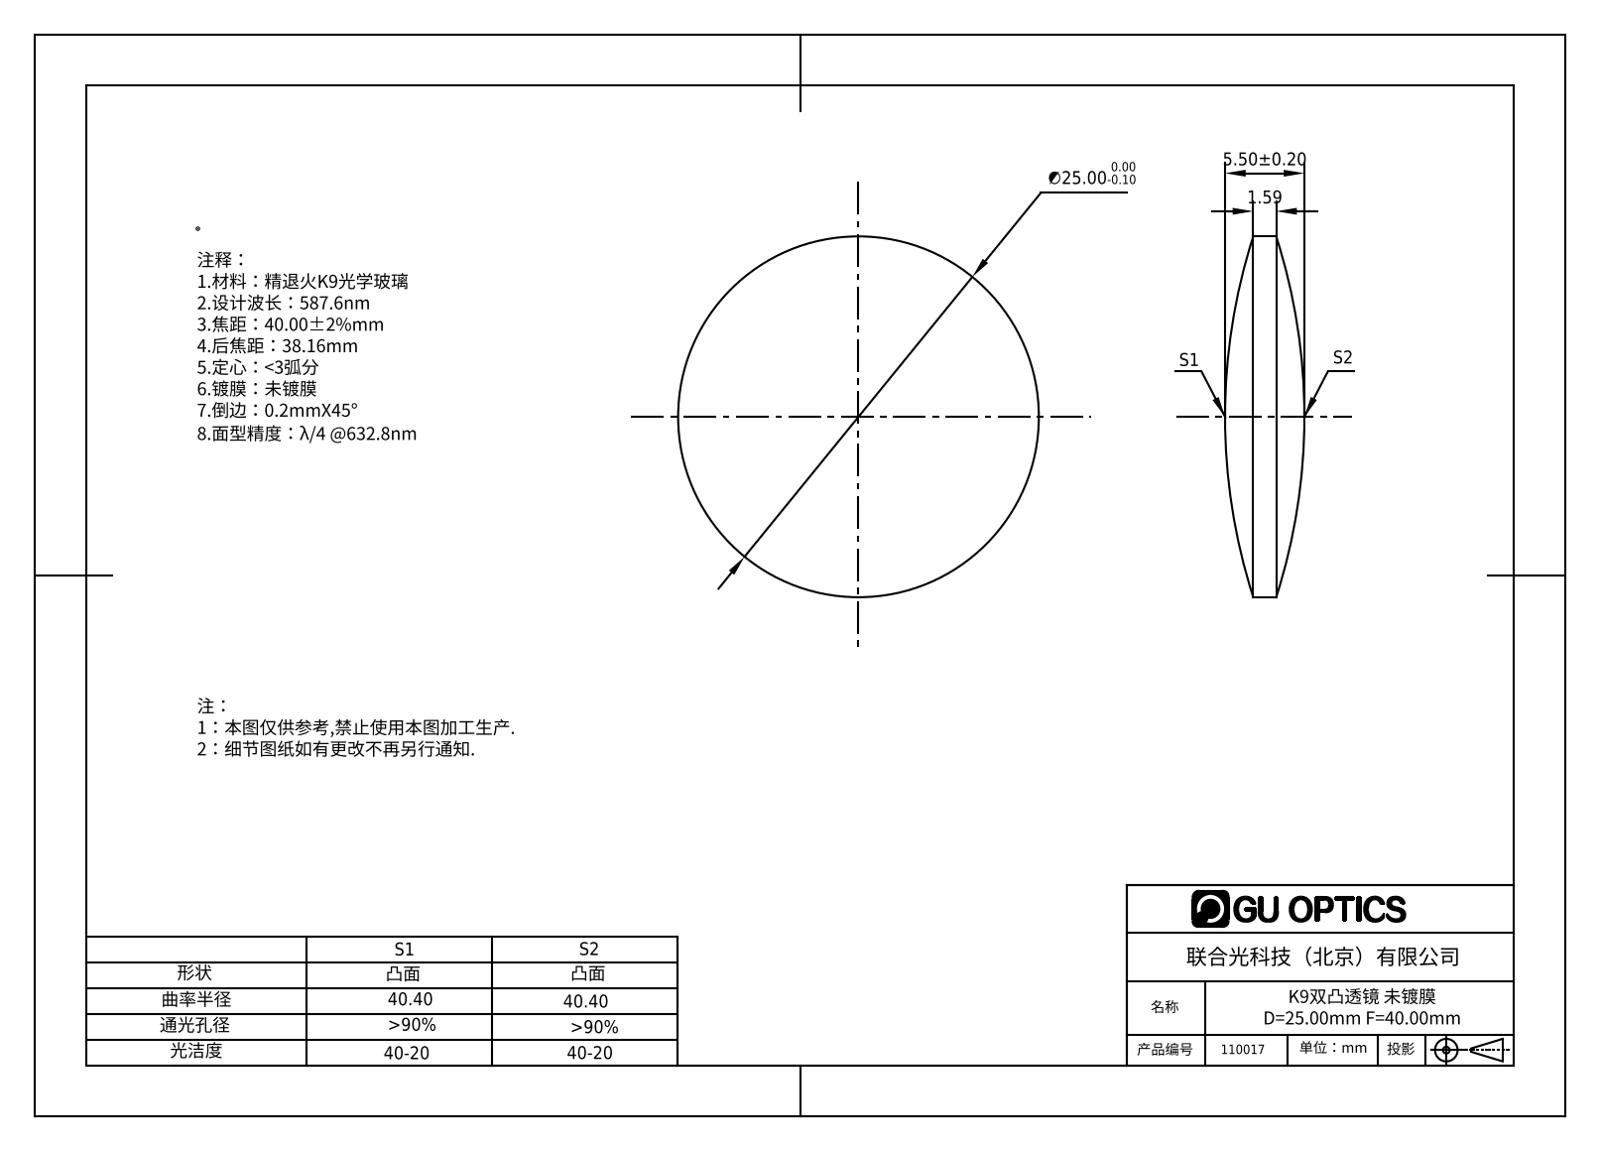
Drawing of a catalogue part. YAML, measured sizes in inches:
part_name: "110017"
step_written_by: "SolidWorks 2016 (CONFIG_CONTROL_DESIGN)"
units: inches
bodies: {solids: 1, faces: 6, planar: 0, cylindrical: 2, other: 4}
overall_size: [0.984, 0.984, 0.217]
volume: 0.107
surface_area: 1.753
round_bosses_or_shafts:
  - {diameter: 0.984, count: 1}
